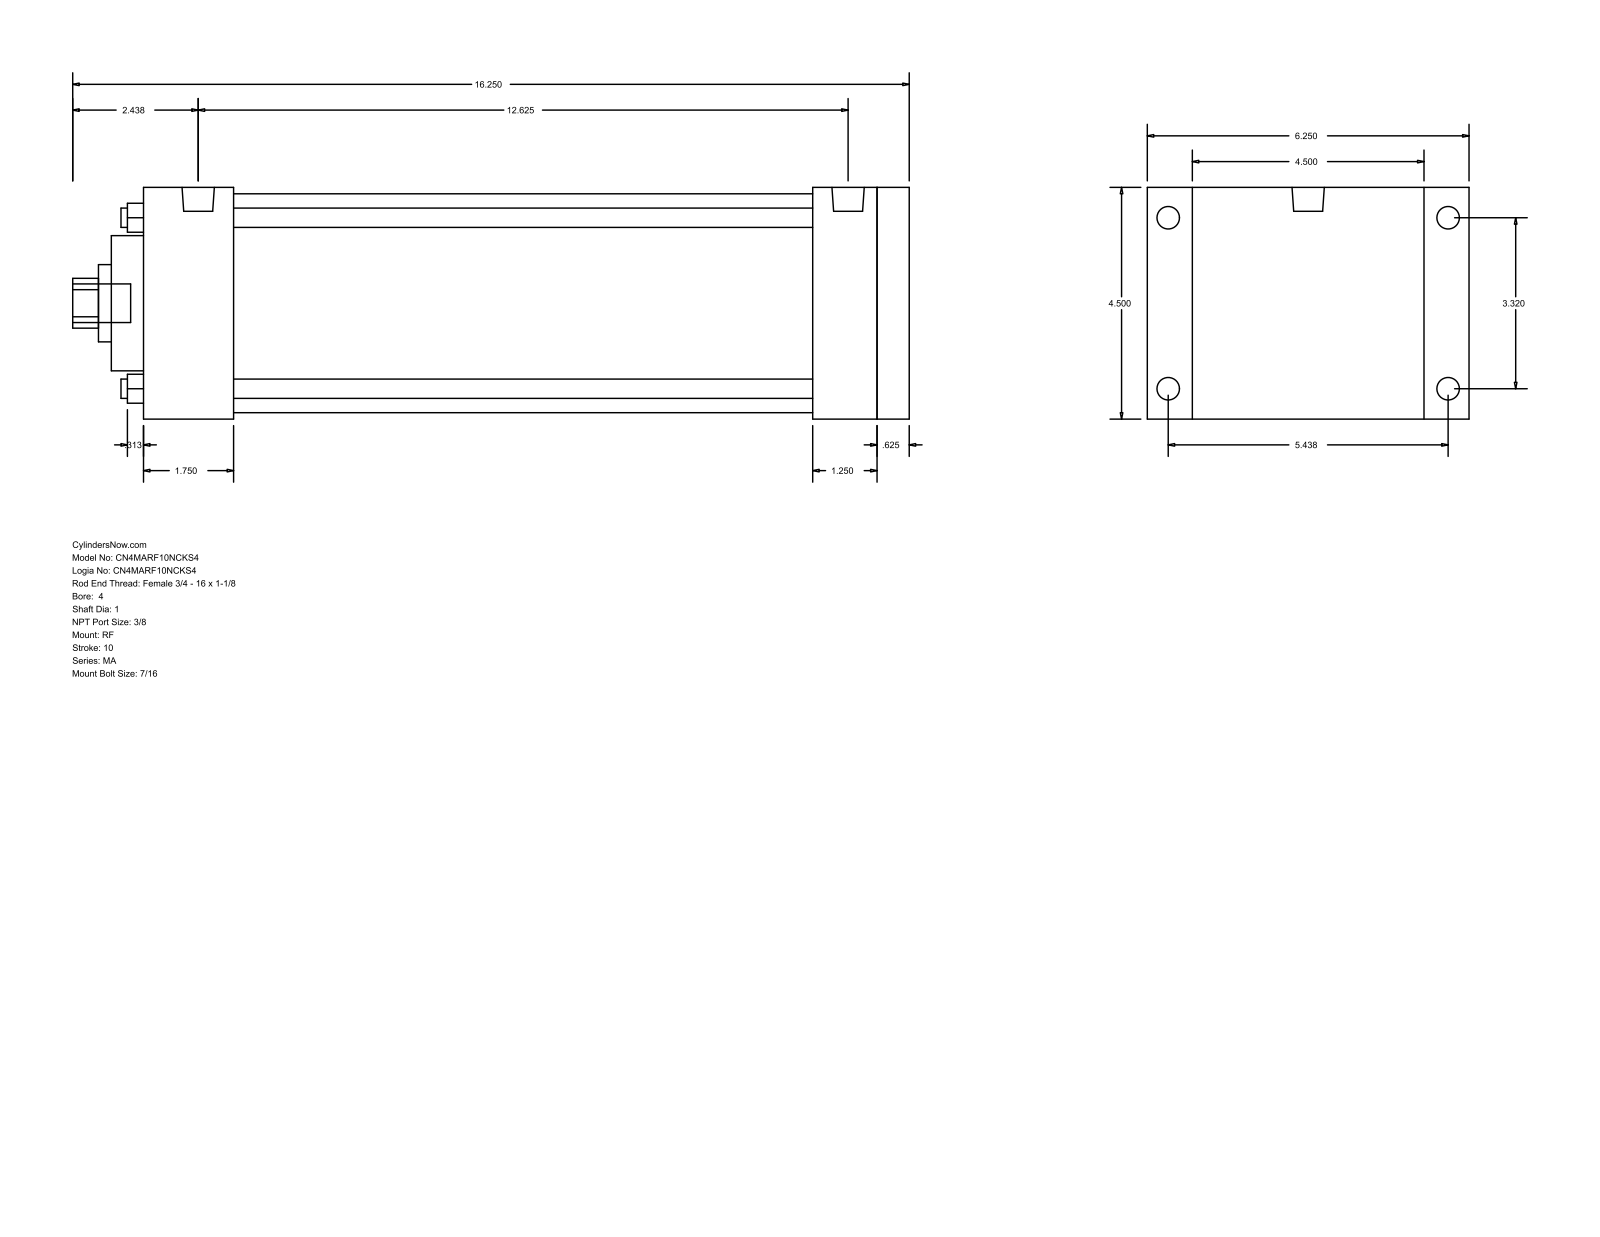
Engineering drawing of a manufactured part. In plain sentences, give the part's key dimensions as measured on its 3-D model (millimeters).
The part is named "MA_RF__0400_1". Its 3-D file was written by "GSSL Pune (CONFIG_CONTROL_DESIGN)". It is 0 solids with 94 faces: 65 planar, 29 cylindrical and 0 other. Overall it measures 412.75 by 158.75 by 114.3 millimeters. Round holes: 4 of diameter 9.53, 1 of diameter 25.4, 1 of diameter 38.1, 1 of diameter 66.67, 1 of diameter 107.95. Round bosses or shafts: 8 of diameter 11.11, 2 of diameter 15.93, 1 of diameter 19.05. Partial cylindrical surfaces (rounded edges, fillets, slot ends): 1 of radius 12.29. The main face-to-face distances are 114.3, 377.83, 15.87, 361.96, 22.23, 136.53, 330.2, 31.76, 47.63, 44.46. The hole center spacings are 59.62, 84.32, 119.25.
